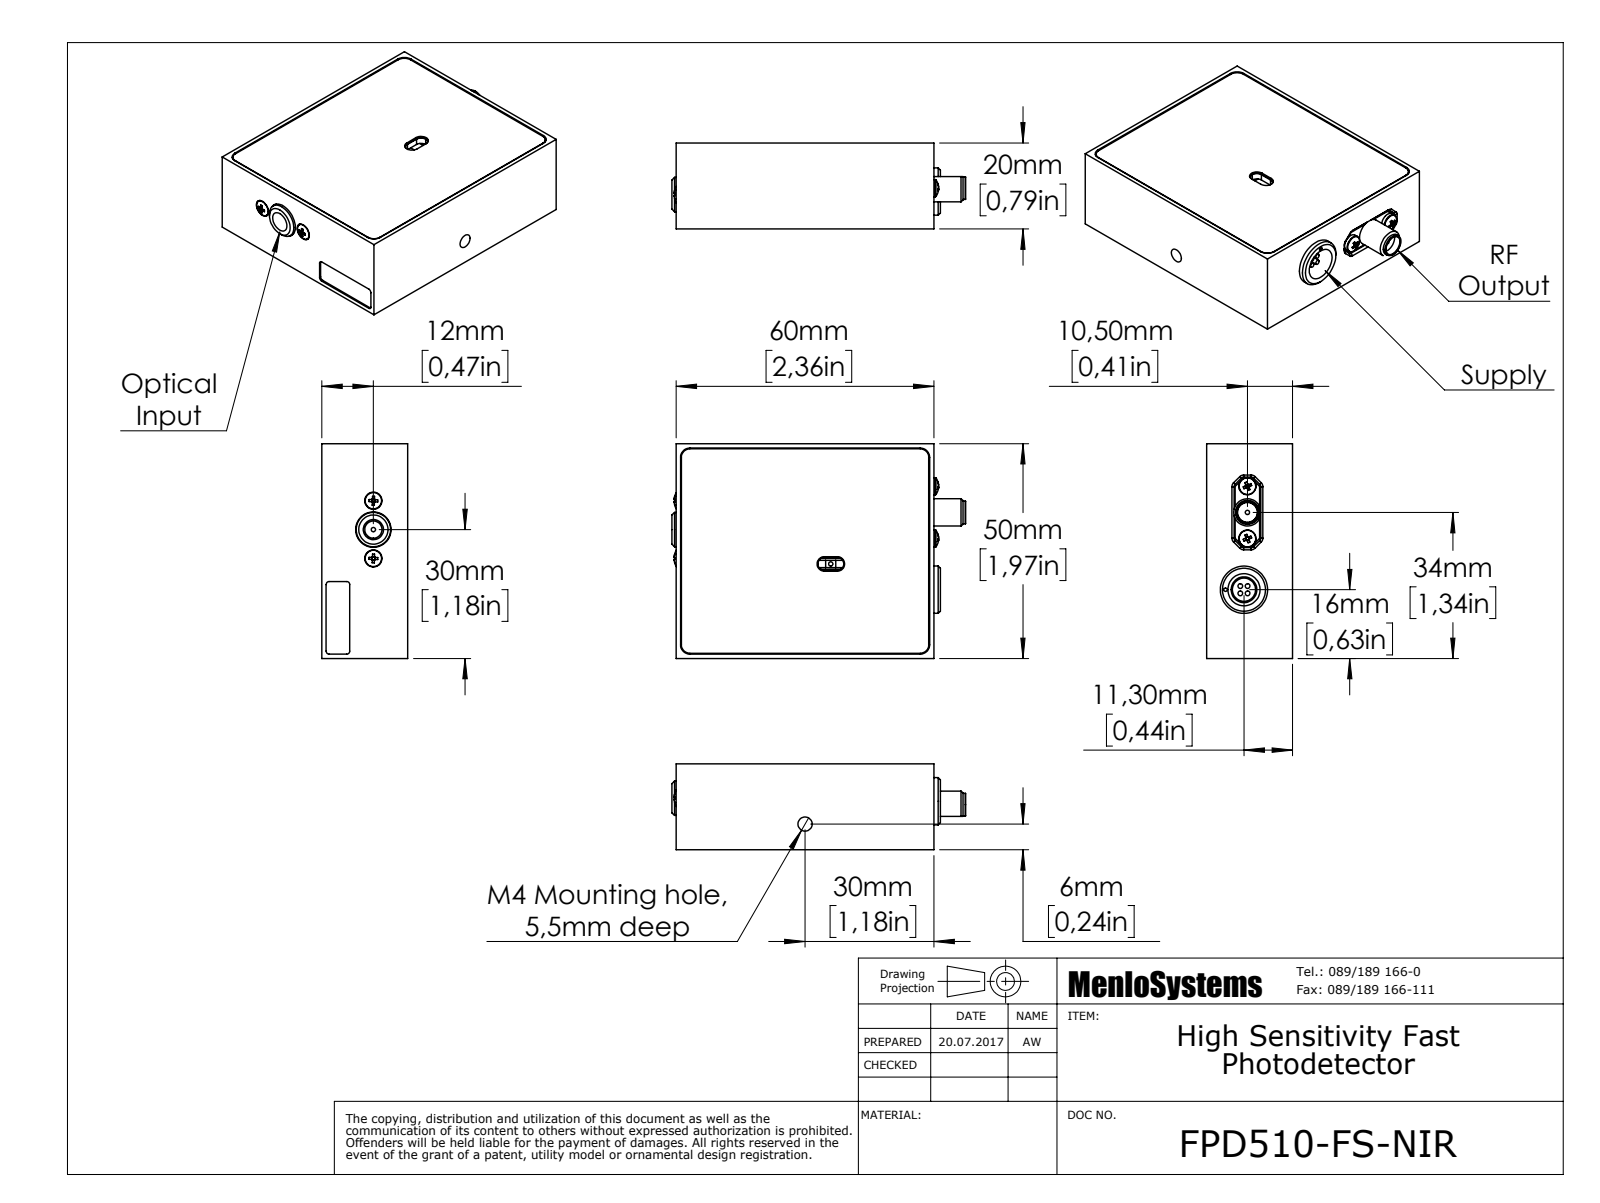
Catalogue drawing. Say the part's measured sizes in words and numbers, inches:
The part is named "FPD510-FS-NIR_170721". Its 3-D file was written by "SolidWorks 2016 (AUTOMOTIVE_DESIGN)". It is 22 solids with 1065 faces: 455 planar, 286 cylindrical and 324 other. Overall it measures 2.693 by 1.969 by 0.787 inches. Its volume is 2.351 cubic inches and its surface area 43.83 square inches. Round holes: 23 of diameter 0.063, 13 of diameter 0.157, 10 of diameter 0.087, 2 of diameter 0.102, 1 of diameter 0.031, 1 of diameter 0.039, 1 of diameter 0.126, 1 of diameter 0.13, 1 of diameter 0.181, 1 of diameter 0.185, 1 of diameter 0.295, 1 of diameter 0.325. Round bosses or shafts: 14 of diameter 0.079, 12 of diameter 0.15, 4 of diameter 0.043, 3 of diameter 0.02, 2 of diameter 0.157, 1 of diameter 0.433, 1 of diameter 0.378, 1 of diameter 0.354. Partial cylindrical surfaces (rounded edges, fillets, slot ends): 26 of radius 0.087, 8 of radius 0.028, 8 of radius 0.031, 8 of radius 0.079, 4 of radius 0.055, 2 of radius 0.059, 1 of radius 0.315. The main face-to-face distances are 0.059, 0.014, 0.77, 0.711, 0.073, 0.783, 0.256, 0.276, 1.969, 0.508. The hole center spacings are 0.166, 0.365, 0.413, 0.589, 0.65, 0.762, 0.787, 0.859.
